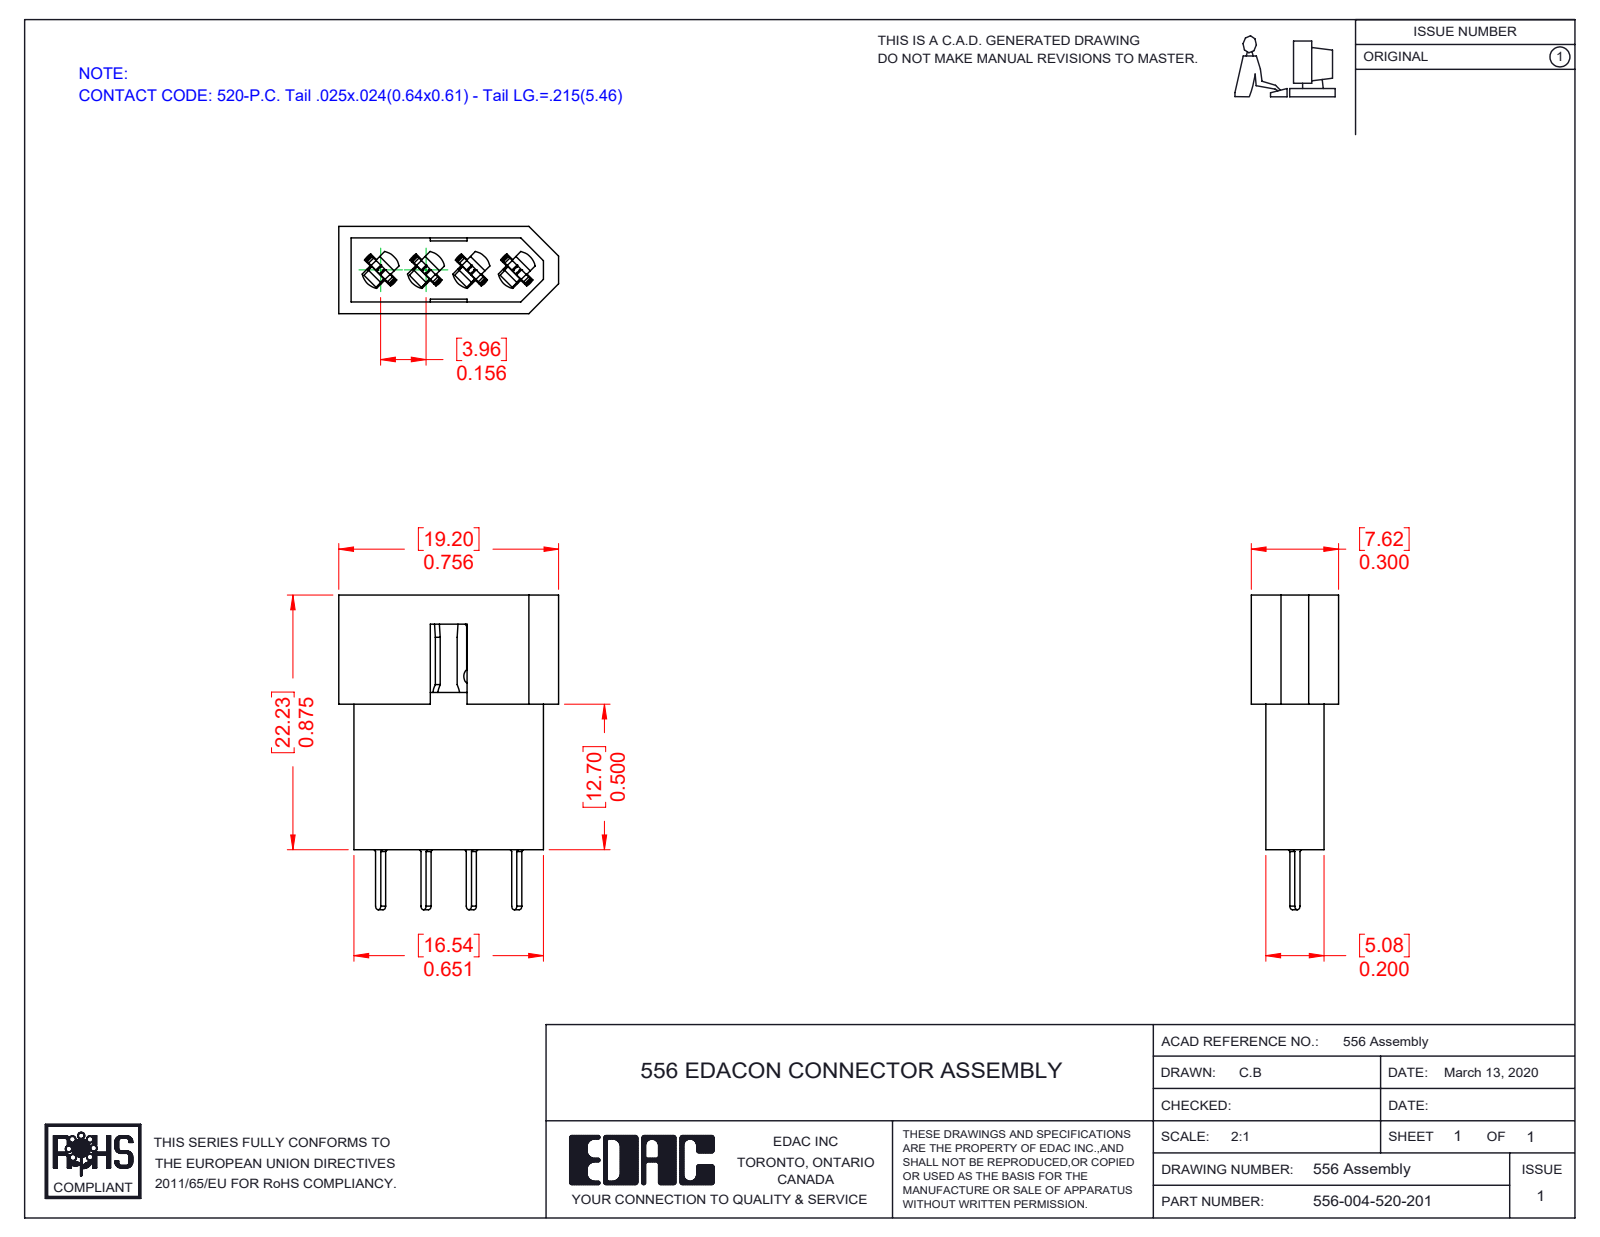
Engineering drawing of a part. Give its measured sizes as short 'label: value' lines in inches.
name: 556-004-520-201; 556-210-001_556-004-000-201; 516-292-001_520 Contact
written by: SolidWorks 2016 (CONFIG_CONTROL_DESIGN)
unit: in
bodies: 5 solids, 421 faces (269 planar, 120 cylindrical, 32 other)
size: 1.081 × 0.756 × 0.3
volume: 0.08 in³; area: 4.405 in²
holes: 4× ⌀0.05, 4× ⌀0.132
rounds: 16× R0.012, 16× R0.022, 8× R0.007, 8× R0.008, 8× R0.016, 8× R0.08, 4× R0.013, 4× R0.065
face distances: 0.11, 0.04, 0.05, 0.25, 0.22, 0.2, 0.26, 0.21, 0.024, 0.134
hole spacings: 0.11, 0.156, 0.111, 0.156, 0.22, 0.221, 0.312, 0.312
